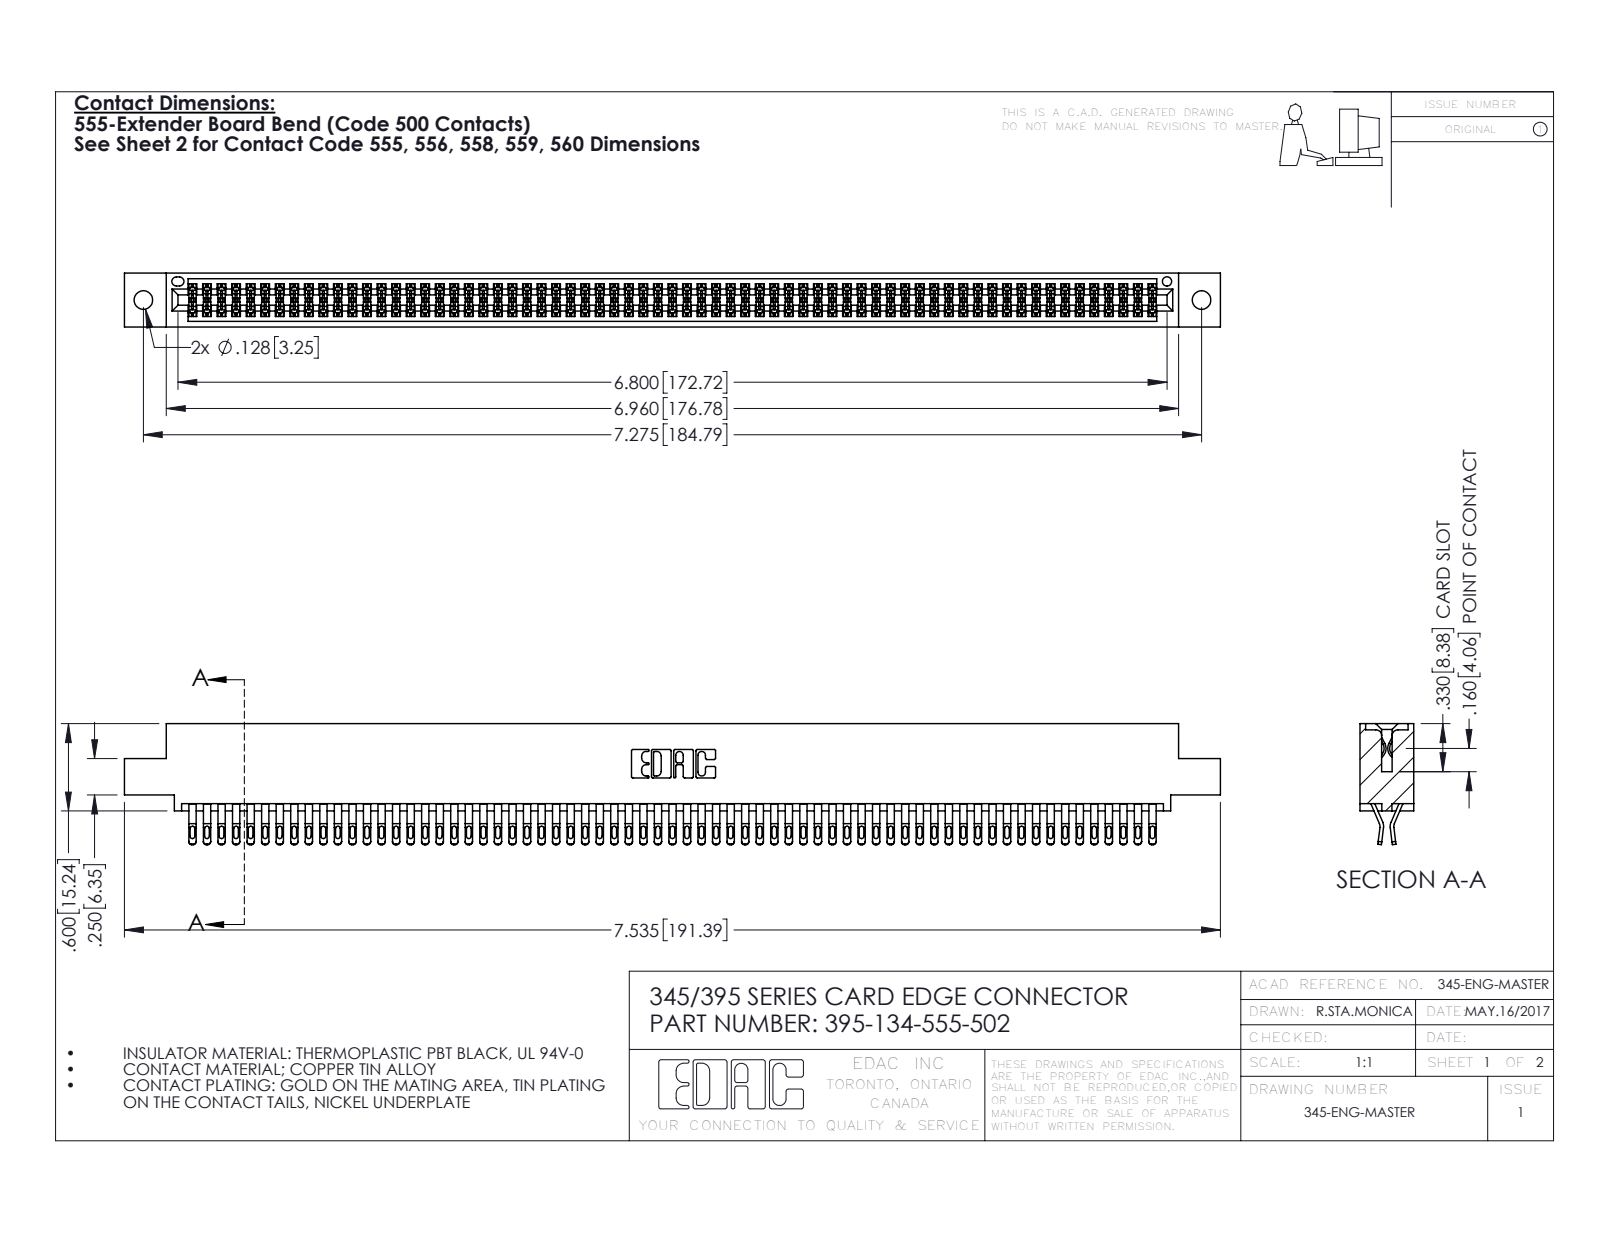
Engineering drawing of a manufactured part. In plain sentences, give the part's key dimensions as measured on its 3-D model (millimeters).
The part is named "345 Part_0.110 Offset - 0.128 Dia; 345-292-001_555 Tail; 395-134-555-502". Its 3-D file was written by "SolidWorks 2016 (CONFIG_CONTROL_DESIGN)". It is 135 solids with 7634 faces: 4238 planar, 3396 cylindrical and 0 other. Overall it measures 191.4 by 21.1 by 9.4 millimeters. Its volume is 19 110 cubic millimeters and its surface area 29 890 square millimeters. Round holes: 2 of diameter 3.3, 1 of diameter 1.6. Partial cylindrical surfaces (rounded edges, fillets, slot ends): 335 of radius 0.4, 268 of radius 0.5, 201 of radius 0.2, 22 of radius 0.3, 6 of radius 0.2, 6 of radius 0.8, 3 of radius 0.7, 2 of radius 0.3. The main face-to-face distances are 7.6, 1.8, 0.6, 9.4, 5.1, 2.5, 6.9, 5.7, 4.4, 3.8. The hole center spacings are 6.9, 178.8, 184.8.
